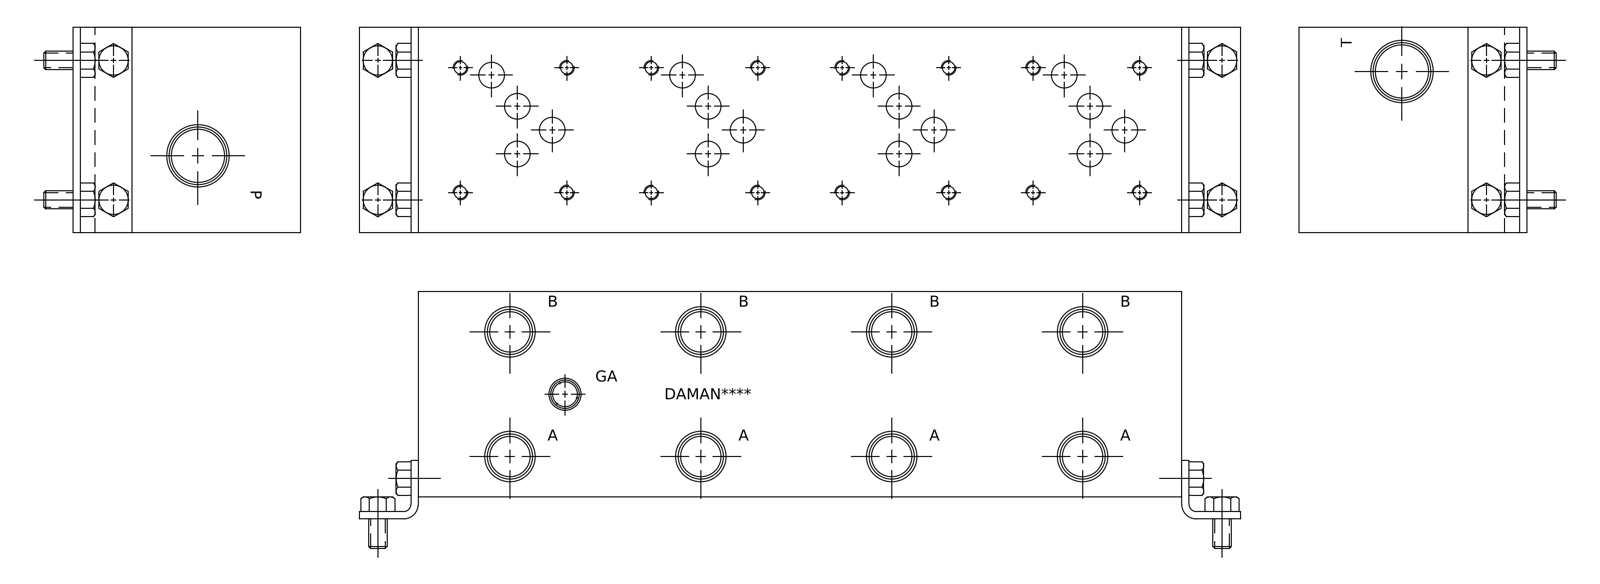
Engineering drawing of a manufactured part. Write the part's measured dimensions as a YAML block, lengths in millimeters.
part_name: "Part_AD05S043P.D02127R3_3D"
step_written_by: "Autodesk Inventor 2020 (AUTOMOTIVE_DESIGN)"
units: millimeters
bodies: {solids: 1, faces: 694, planar: 395, cylindrical: 78, other: 221}
overall_size: [330.2, 88.9, 88.9]
volume: 2517000
surface_area: 156325
round_holes:
  - {diameter: 5.11, count: 16}
  - {diameter: 6.35, count: 16}
  - {diameter: 11.13, count: 16}
  - {diameter: 17.48, count: 8}
  - {diameter: 21.59, count: 8}
  - {diameter: 6.53, count: 2}
  - {diameter: 7.92, count: 2}
  - {diameter: 23.01, count: 2}
  - {diameter: 26.92, count: 2}
  - {diameter: 10.72, count: 1}
  - {diameter: 13.87, count: 1}
face_to_face_distances: [88.9, 330.2, 73.53, 15.37, 15.85, 314.35, 15.33, 88.86, 69.85, 19.05]
hole_center_spacings: [82.55, 165.1, 98.63, 18.27, 46.05, 68.25, 70.95, 98.64]
